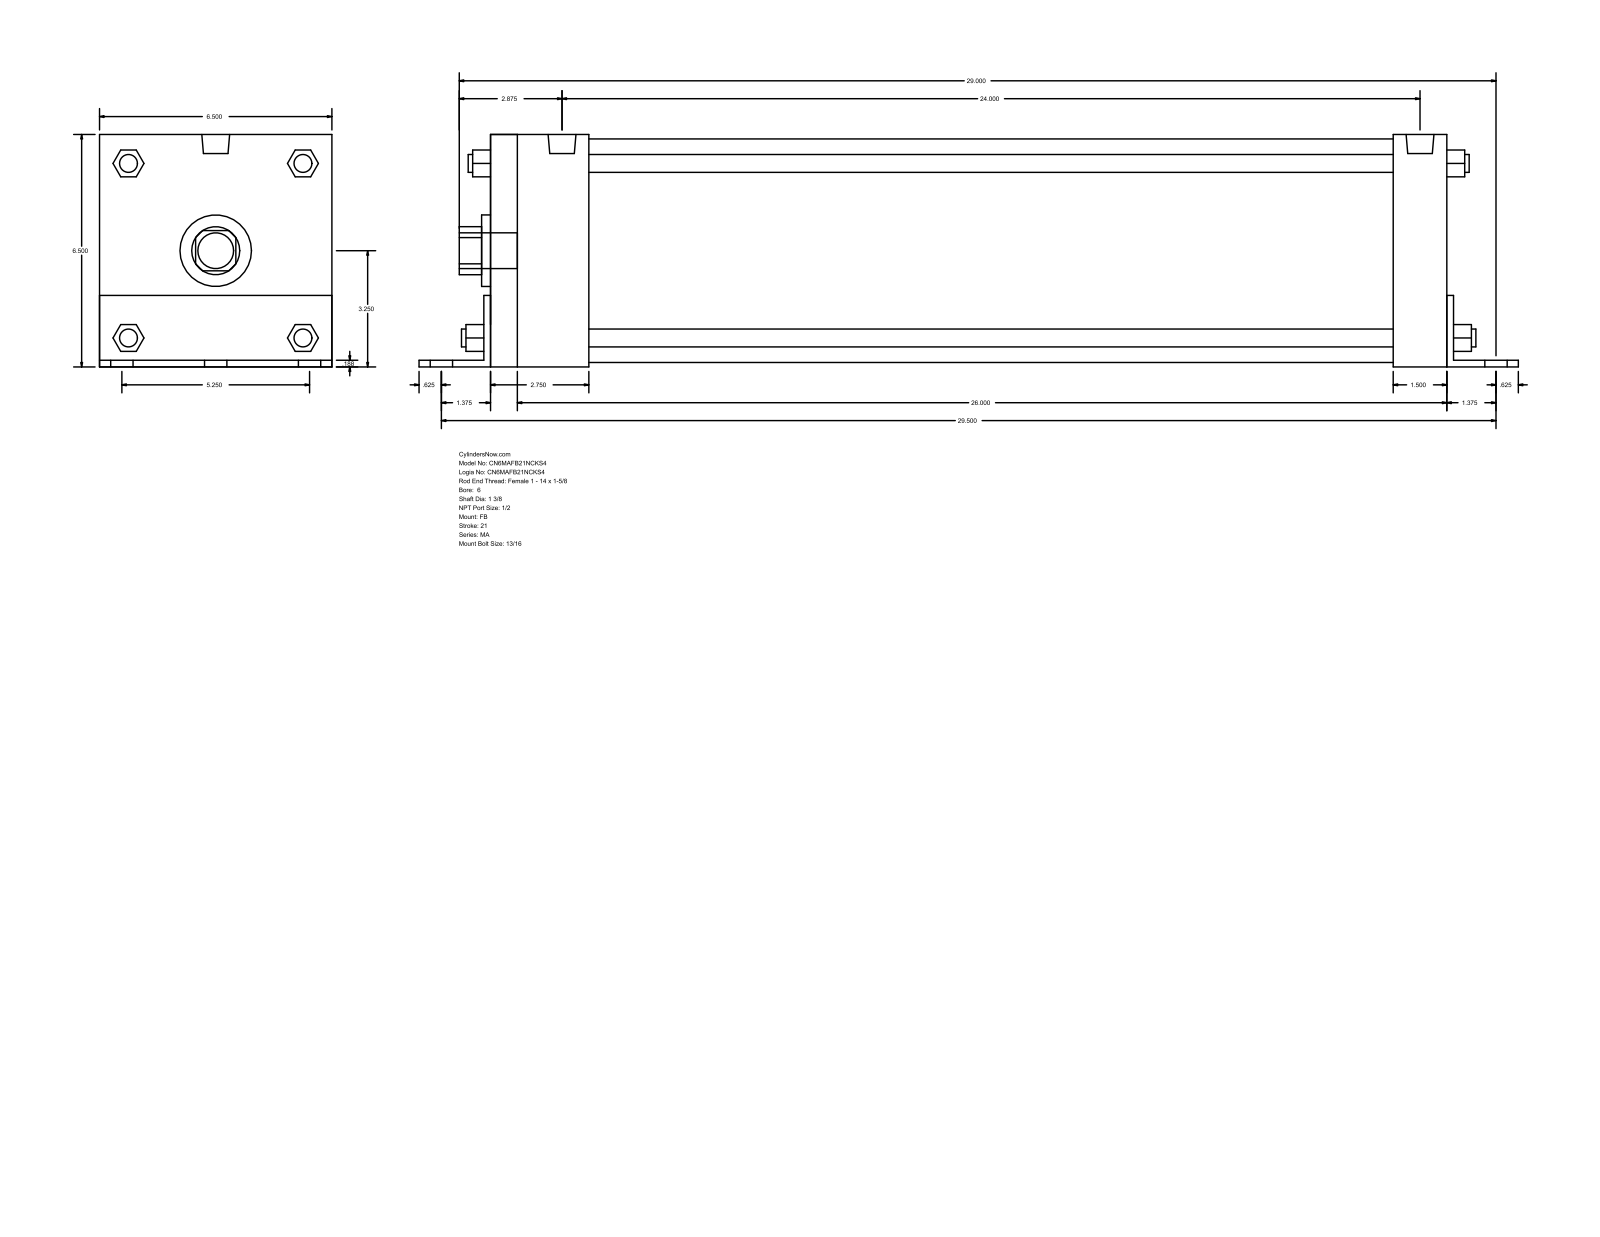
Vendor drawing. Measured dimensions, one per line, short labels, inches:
name: MA_FB__0600_1.375
written by: GSSL Pune (CONFIG_CONTROL_DESIGN)
unit: in
bodies: 0 solids, 140 faces (105 planar, 35 cylindrical, 0 other)
size: 30.625 × 6.502 × 6.5
holes: 1× ⌀1.375, 1× ⌀2, 1× ⌀6.25
bosses: 6× ⌀0.813, 4× ⌀0.687, 4× ⌀0.5, 2× ⌀0.778, 1× ⌀1
rounds: 1× R0.672, 1× R1.262
face distances: 6.5, 0.187, 26.625, 6.502, 0.185, 6.315, 0.188, 1.5, 26.813, 27
